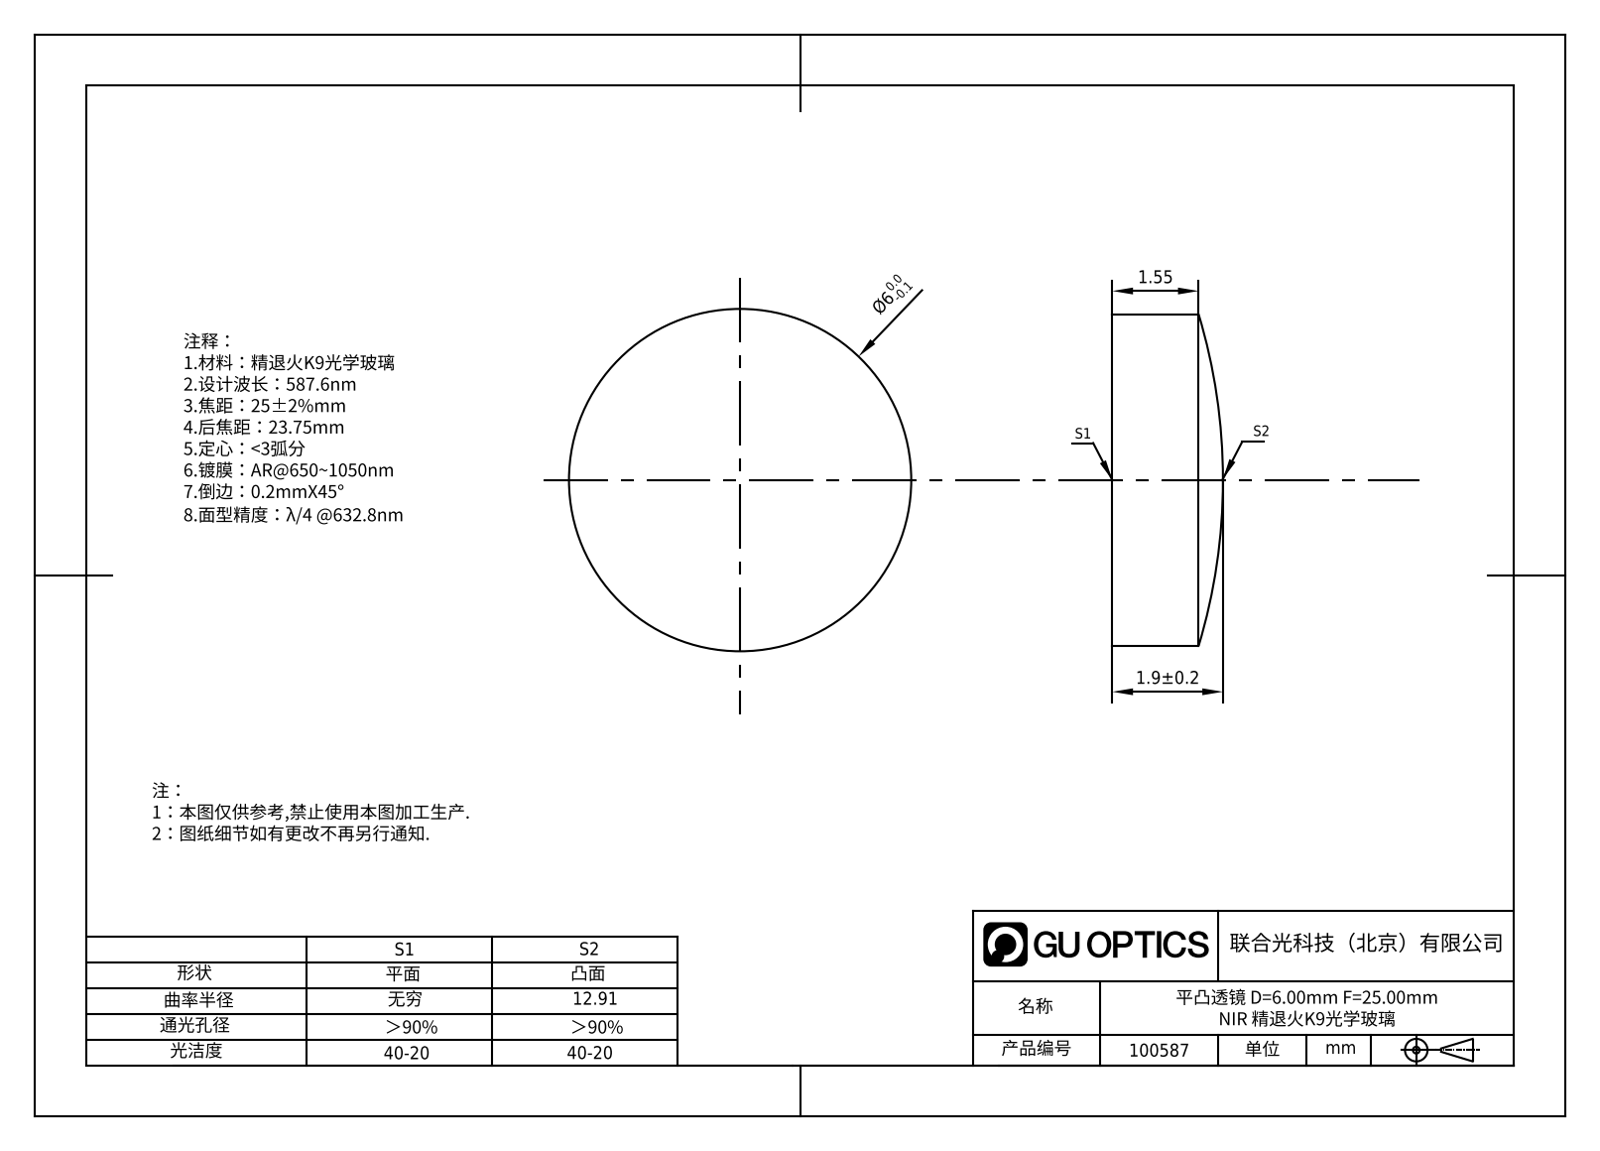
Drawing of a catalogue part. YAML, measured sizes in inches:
part_name: "100587"
step_written_by: "SolidWorks 2020 (CONFIG_CONTROL_DESIGN)"
units: inches
bodies: {solids: 1, faces: 5, planar: 1, cylindrical: 2, other: 2}
overall_size: [0.236, 0.236, 0.075]
volume: 0.003
surface_area: 0.13
round_bosses_or_shafts:
  - {diameter: 0.236, count: 1}
